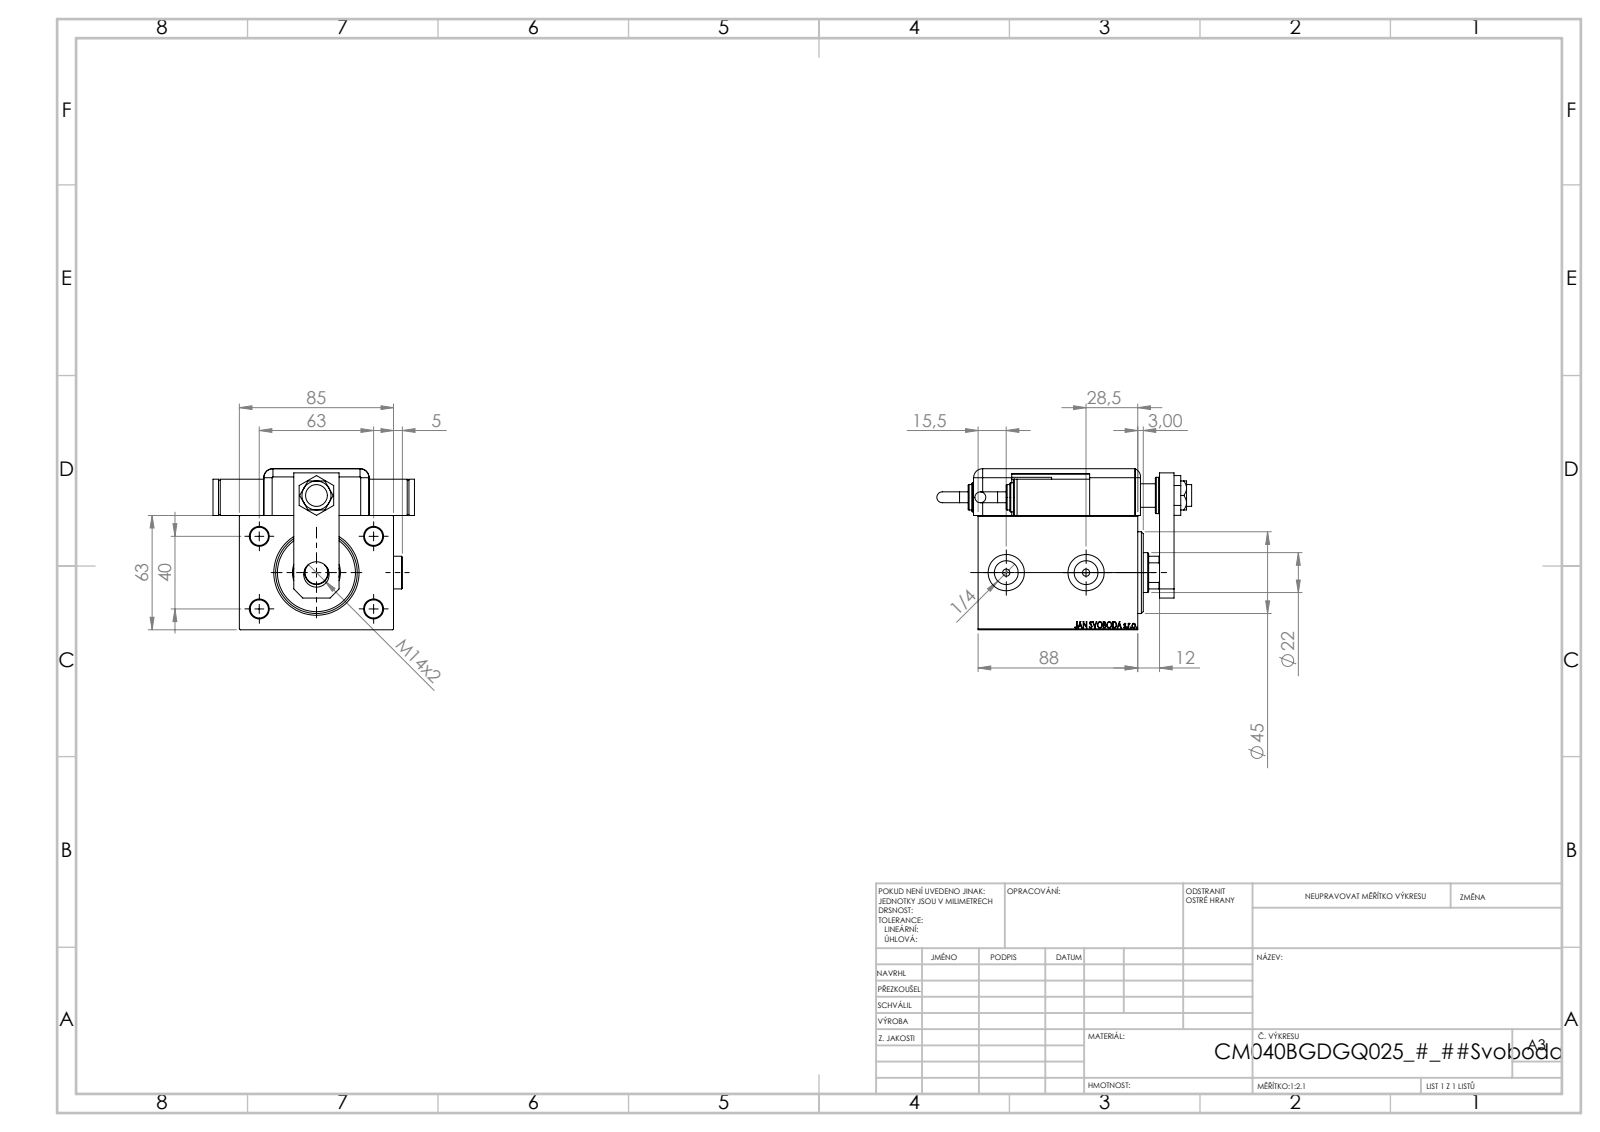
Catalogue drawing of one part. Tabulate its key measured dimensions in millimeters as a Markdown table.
| quantity | value |
| --- | --- |
| part name | V450CM_VC_B; NUT_D13; V450CM_B_VCP; MAGNETIC SWITCH Q (+7 more) |
| STEP written by | SolidWorks 2019 (CONFIG_CONTROL_DESIGN) |
| units | millimeters |
| bodies | 15 solids, 1319 faces (641 planar, 125 cylindrical, 553 other) |
| overall size | 140.46 × 111 × 88.8 |
| volume | 569 247 mm³ |
| surface area | 123 212 mm² |
| round holes (diameter × count) | 4 × 4, 10 × 4, 8 × 2, 13.16 × 2, 14 × 2, 20 × 2, 12 × 1, 12.5 × 1, 13 × 1, 22 × 1, 25.5 × 1, 26.5 × 1 |
| round bosses / shafts (diameter × count) | 20 × 3, 18 × 2, 16 × 2, 14 × 2, 6 × 2 |
| partial cylindrical surfaces (radius × count) | 5 × 9, 10 × 1, 10.5 × 1 |
| main face-to-face distances | 3, 63, 13.5, 85, 12, 88, 83, 20, 88.8, 1.5 |
| hole center spacings | 37.31, 36.79, 37.86, 38.71, 40, 63, 69.99, 74.63 |
